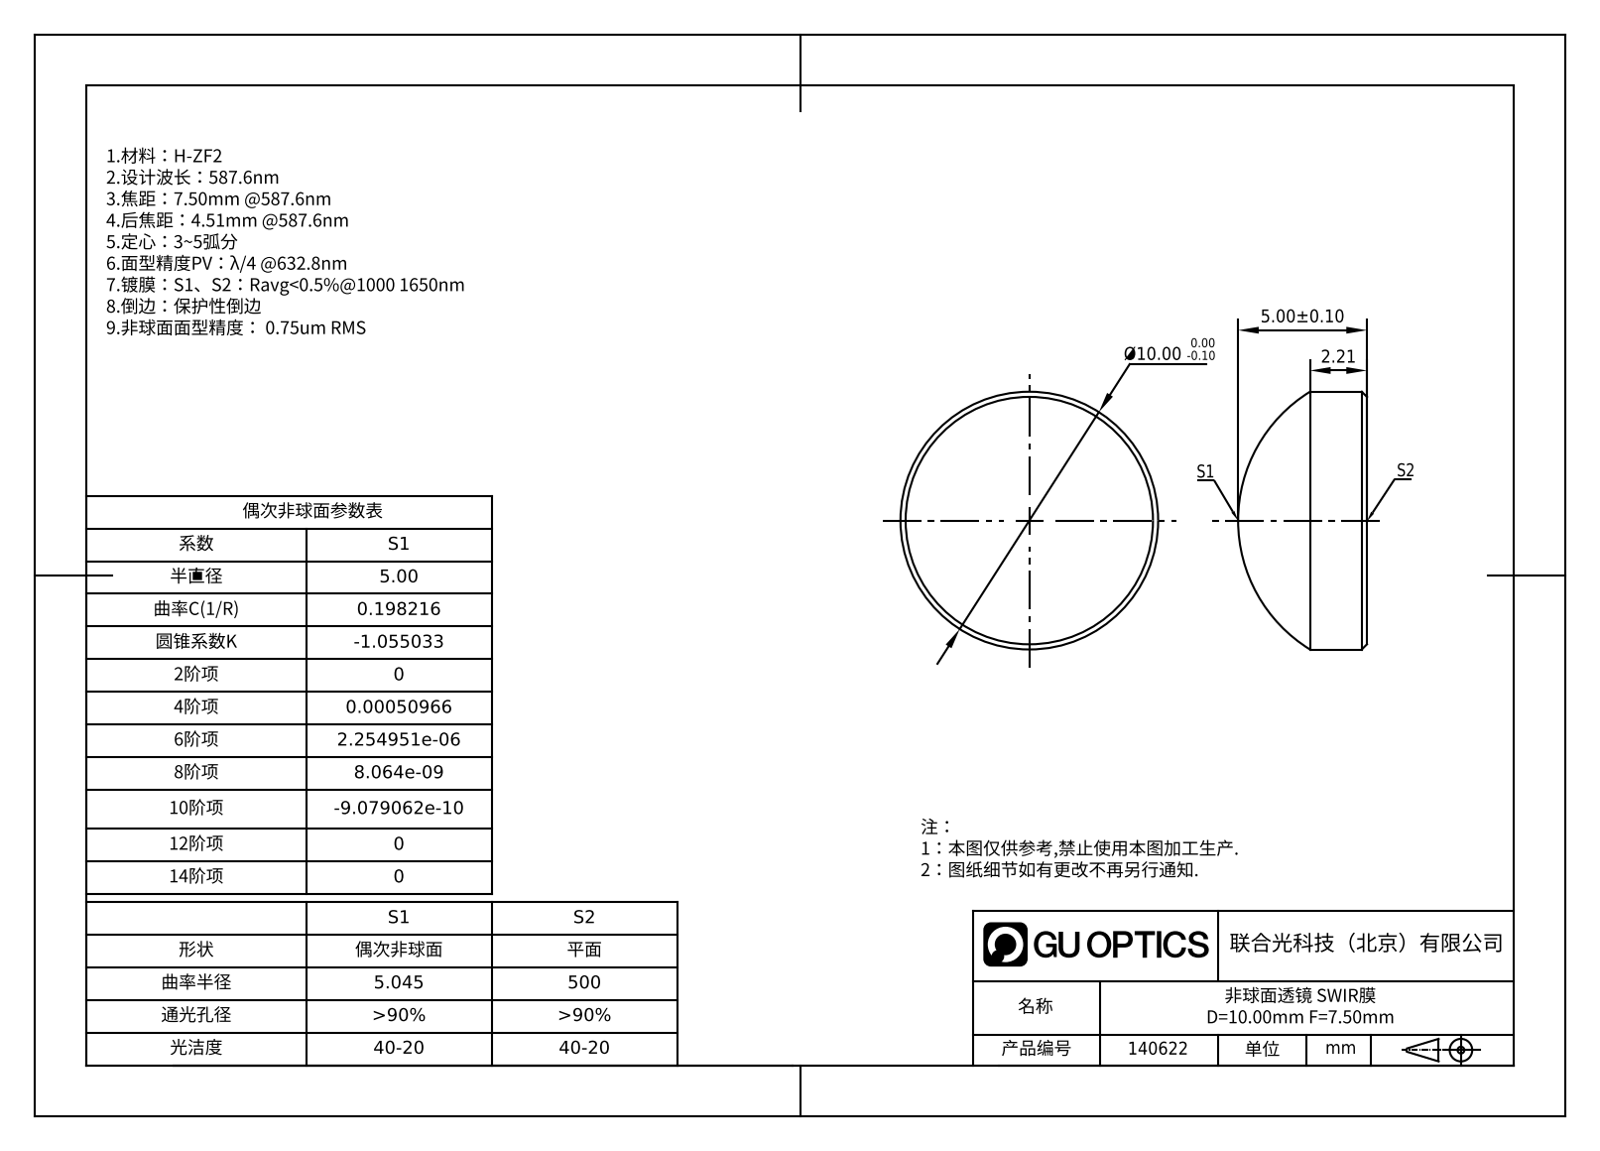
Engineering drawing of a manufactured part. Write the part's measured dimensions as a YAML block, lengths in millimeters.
part_name: "GLA11-010-7.5-SWIR"
step_written_by: "SolidWorks 2022 (AUTOMOTIVE_DESIGN)"
units: millimeters
bodies: {solids: 1, faces: 7, planar: 1, cylindrical: 2, other: 4}
overall_size: [10, 10, 5]
volume: 294
surface_area: 247
round_bosses_or_shafts:
  - {diameter: 10, count: 1}
